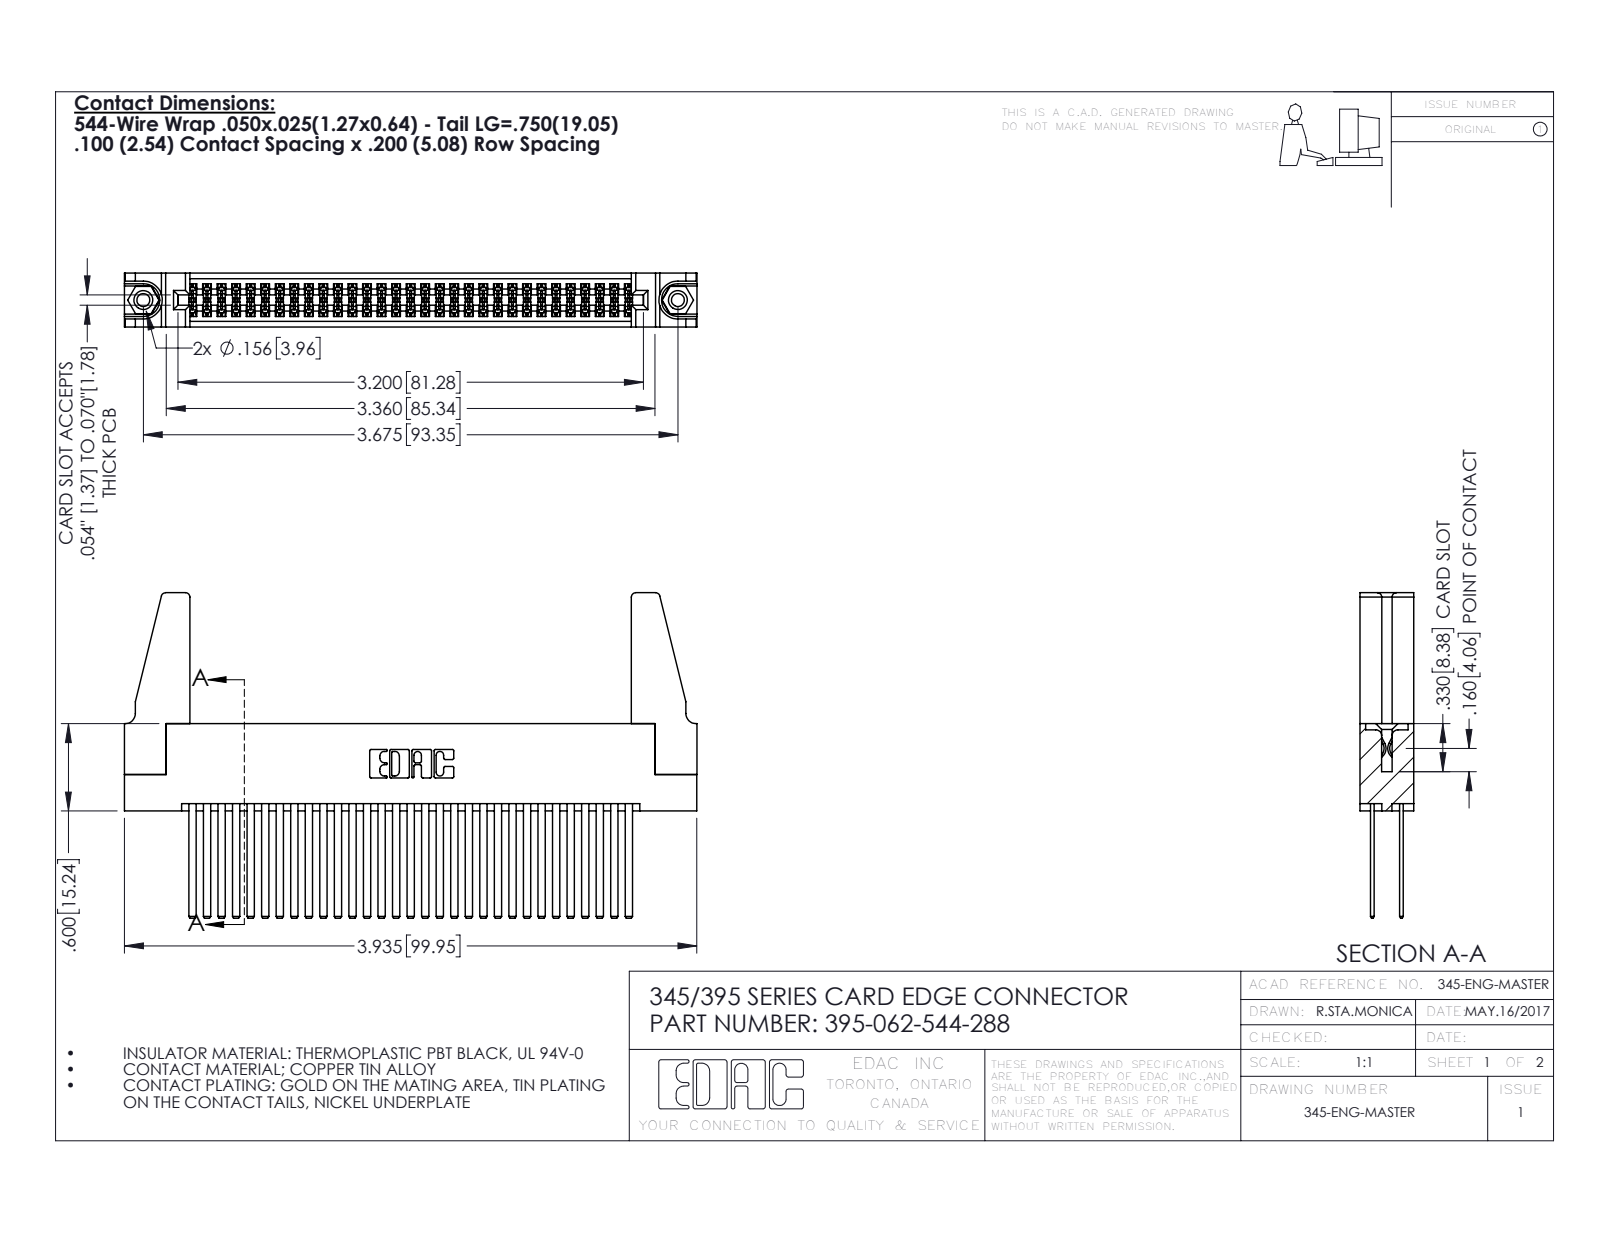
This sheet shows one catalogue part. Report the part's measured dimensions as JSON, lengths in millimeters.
{"part_name": "345 Part_Flush Mounting Lugs - 0.156 Dia-TH; 345-250-001_345-250-001-102; 395-062-544-288; 345-220-078_345-220-088 (+1 more)", "step_written_by": "SolidWorks 2016 (CONFIG_CONTROL_DESIGN)", "units": "millimeters", "bodies": {"solids": 67, "faces": 2978, "planar": 1950, "cylindrical": 1012, "other": 16}, "overall_size": [100, 56.8, 9.4], "volume_mm3": 13700, "surface_area_mm2": 20950, "round_holes": [[2.3, 2], [3.2, 2], [4, 2], [1.6, 1]], "round_bosses_or_shafts": [[3.9, 2]], "partial_cylinders_radius": [[0.2, 93], [0.3, 22], [0.8, 8], [0.2, 6], [0.8, 6], [0.7, 3], [0.4, 2], [0.5, 2]], "face_to_face_distances": [1.8, 7.6, 5.1, 2.5, 6.9, 0.6, 9.4, 5.7, 4.4, 1.3], "hole_center_spacings": [6.9, 87.4, 93.3]}
